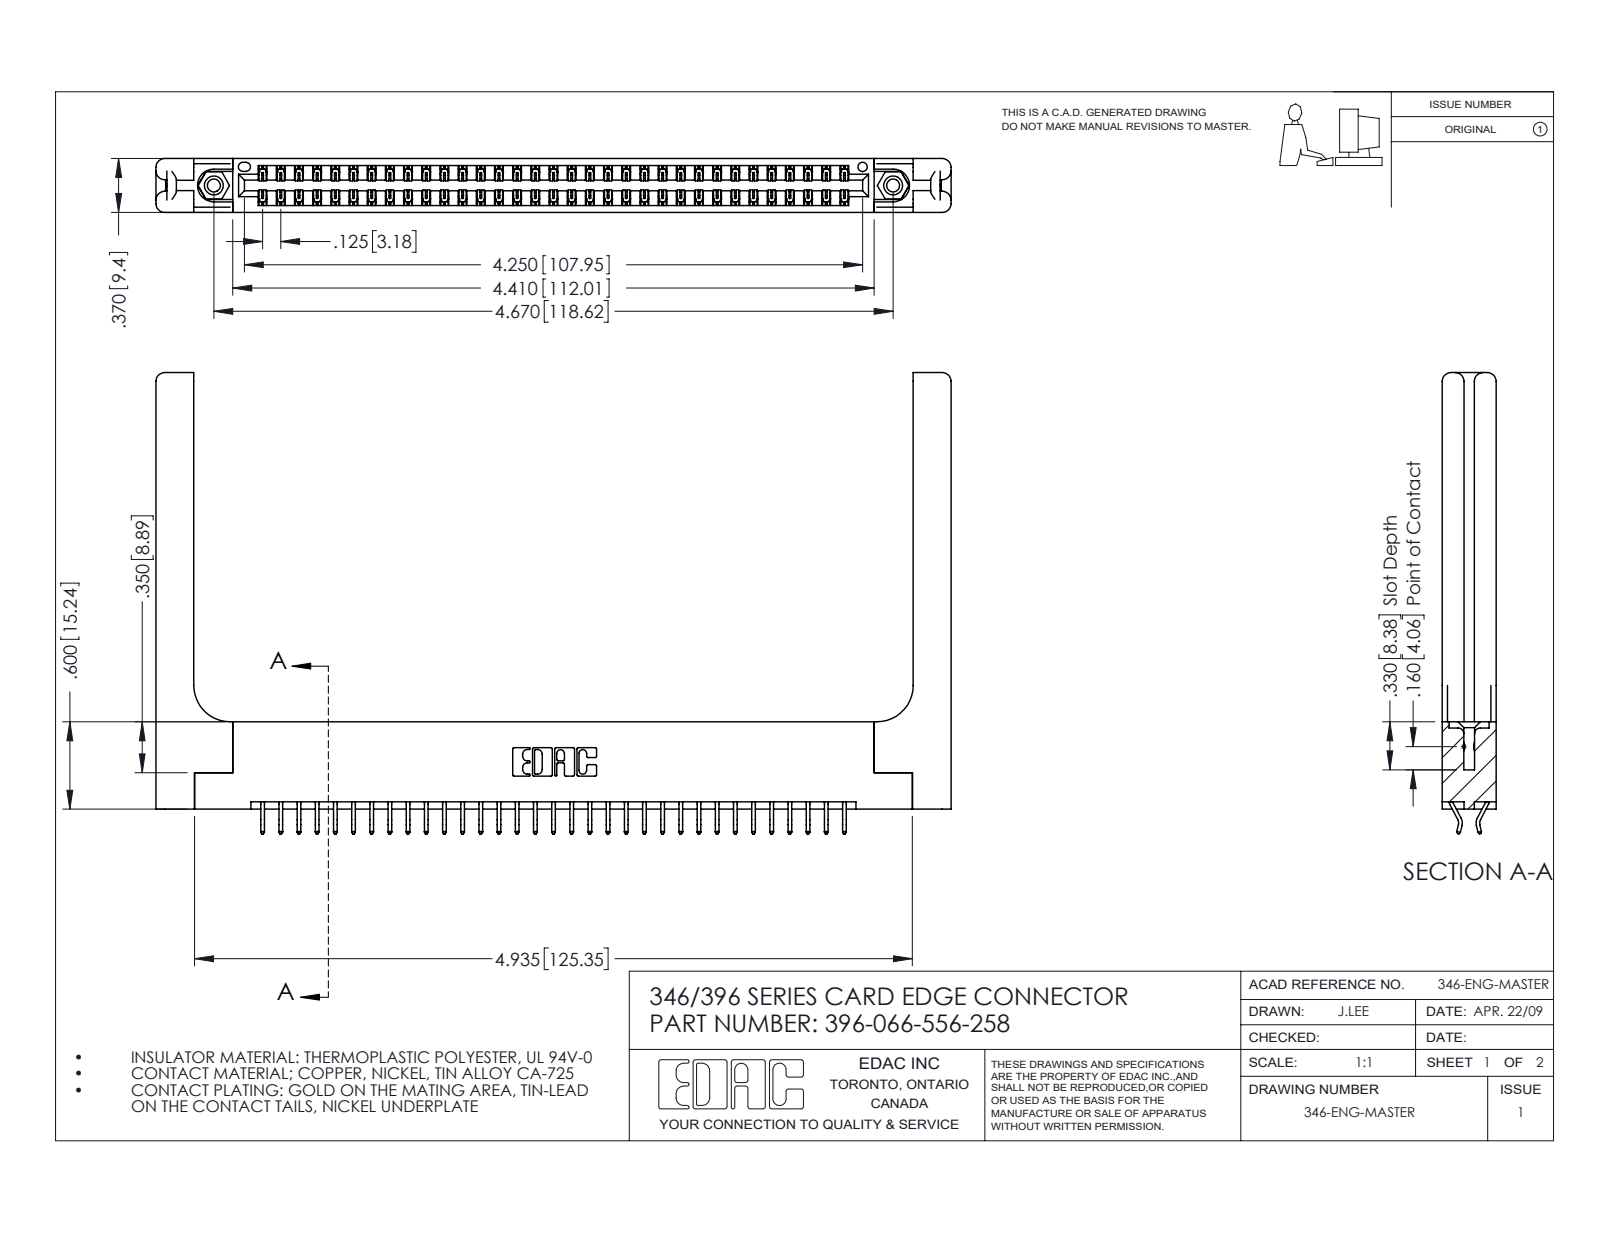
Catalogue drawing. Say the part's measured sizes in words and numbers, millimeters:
The part is named "345-250-001_345-250-001-102; 345-292-001_556 Tail; 346-220-058_345-220-058; 346 Part_Flush Mounting Lugs - 0.156 Dia-TH (+1 more)". Its 3-D file was written by "SolidWorks 2016 (CONFIG_CONTROL_DESIGN)". It is 71 solids with 4206 faces: 2798 planar, 1348 cylindrical and 60 other. Overall it measures 138.8 by 80.5 by 9.4 millimeters. Its volume is 20 960 cubic millimeters and its surface area 23 280 square millimeters. Round holes: 2 of diameter 2.3, 2 of diameter 3.2, 2 of diameter 4, 1 of diameter 1.6. Round bosses or shafts: 2 of diameter 3.9. Partial cylindrical surfaces (rounded edges, fillets, slot ends): 99 of radius 0.2, 22 of radius 0.3, 16 of radius 1.5, 6 of radius 0.2, 6 of radius 0.8, 3 of radius 0.7, 2 of radius 0.3, 2 of radius 0.4. The main face-to-face distances are 9.4, 1.2, 8.2, 1.8, 3.8, 3.8, 6.4, 0.6, 7.6, 7. The hole center spacings are 6.2, 113.3, 118.6.
